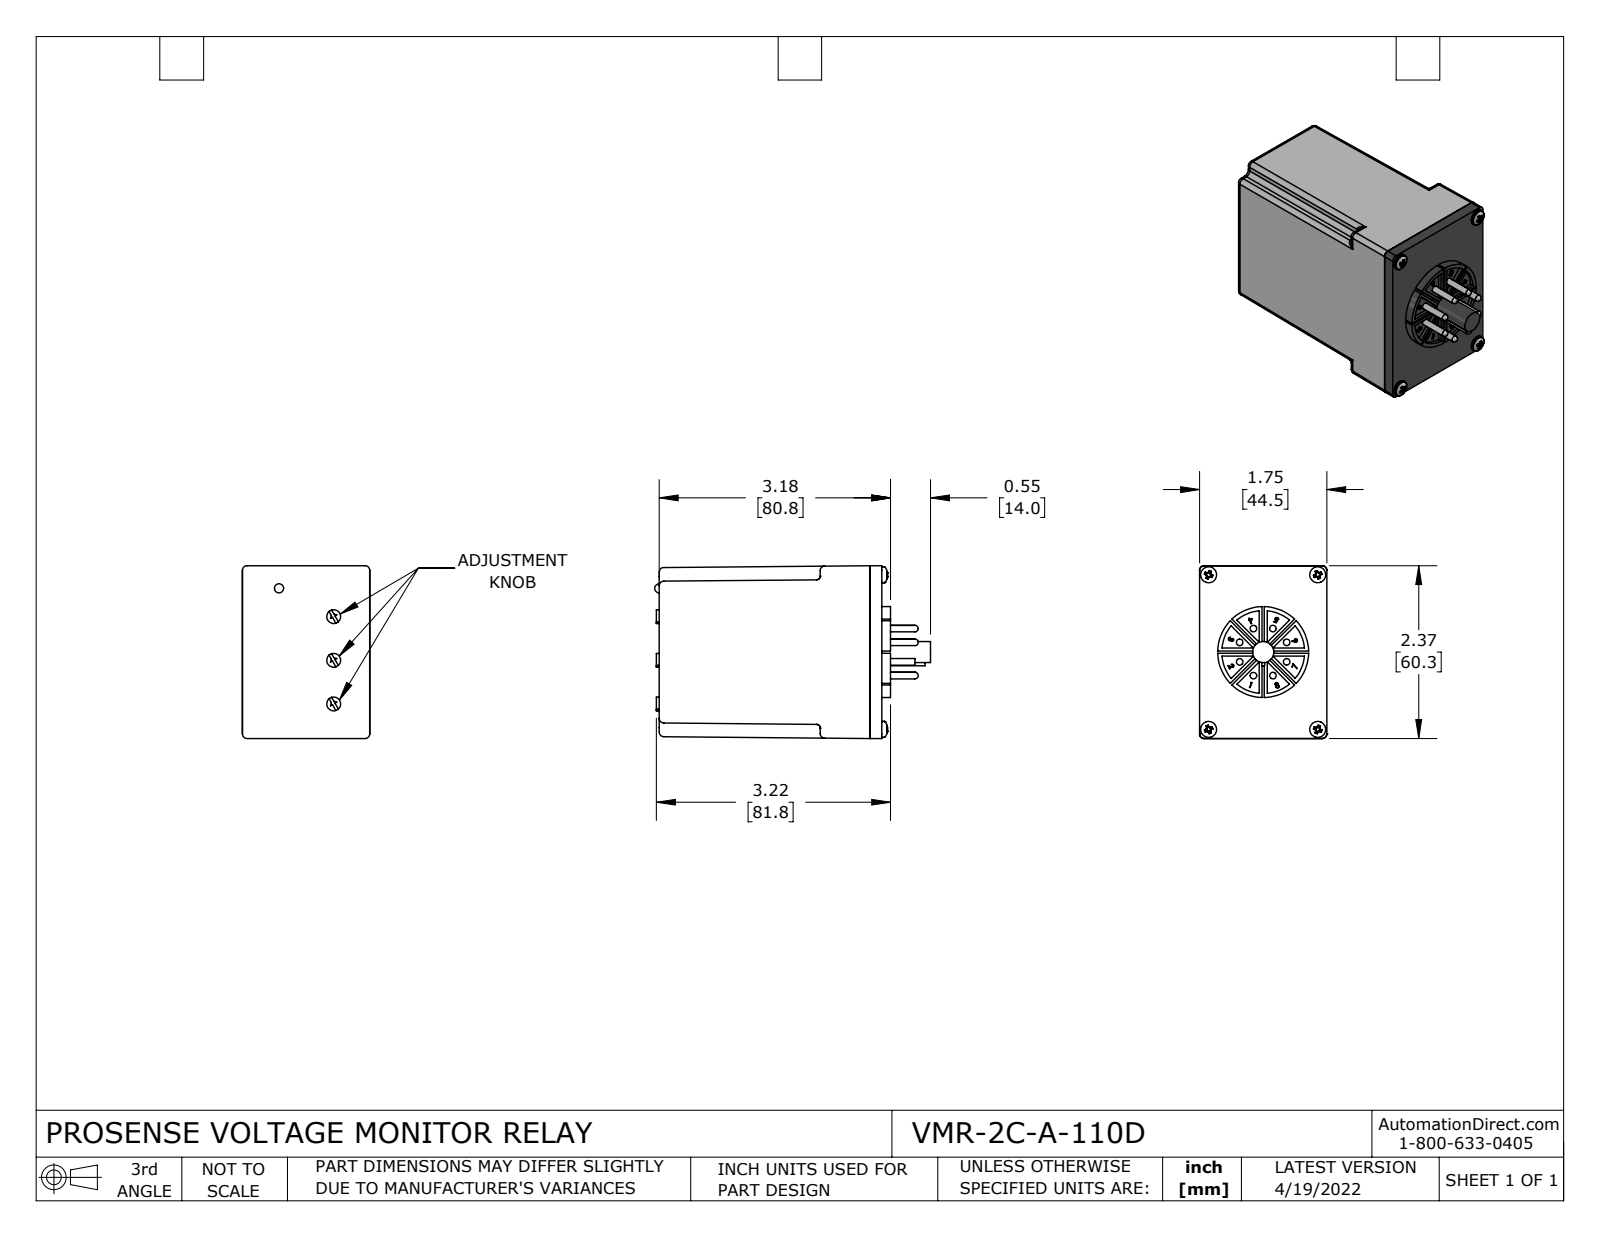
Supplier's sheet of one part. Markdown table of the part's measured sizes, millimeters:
| quantity | value |
| --- | --- |
| part name | VMR-2C-A-110D |
| STEP written by | SolidWorks 2021 (CONFIG_CONTROL_DESIGN) |
| units | millimeters |
| bodies | 18 solids, 574 faces (249 planar, 170 cylindrical, 155 other) |
| overall size | 96.3 × 60.3 × 44.5 |
| volume | 200 700 mm³ |
| surface area | 28 850 mm² |
| round holes (diameter × count) | 3.2 × 4 |
| round bosses / shafts (diameter × count) | 2.3 × 8, 5.6 × 4, 4.8 × 3, 31.8 × 1, 7.4 × 1 |
| partial cylindrical surfaces (radius × count) | 1.6 × 32, 0.1 × 8, 1.3 × 4, 14.5 × 1 |
| main face-to-face distances | 73.7, 4.1, 77.7, 1.8, 5.8, 79.5, 4.8, 1.3, 3, 7.1 |
| hole center spacings | 38.1, 54, 66.1 |
